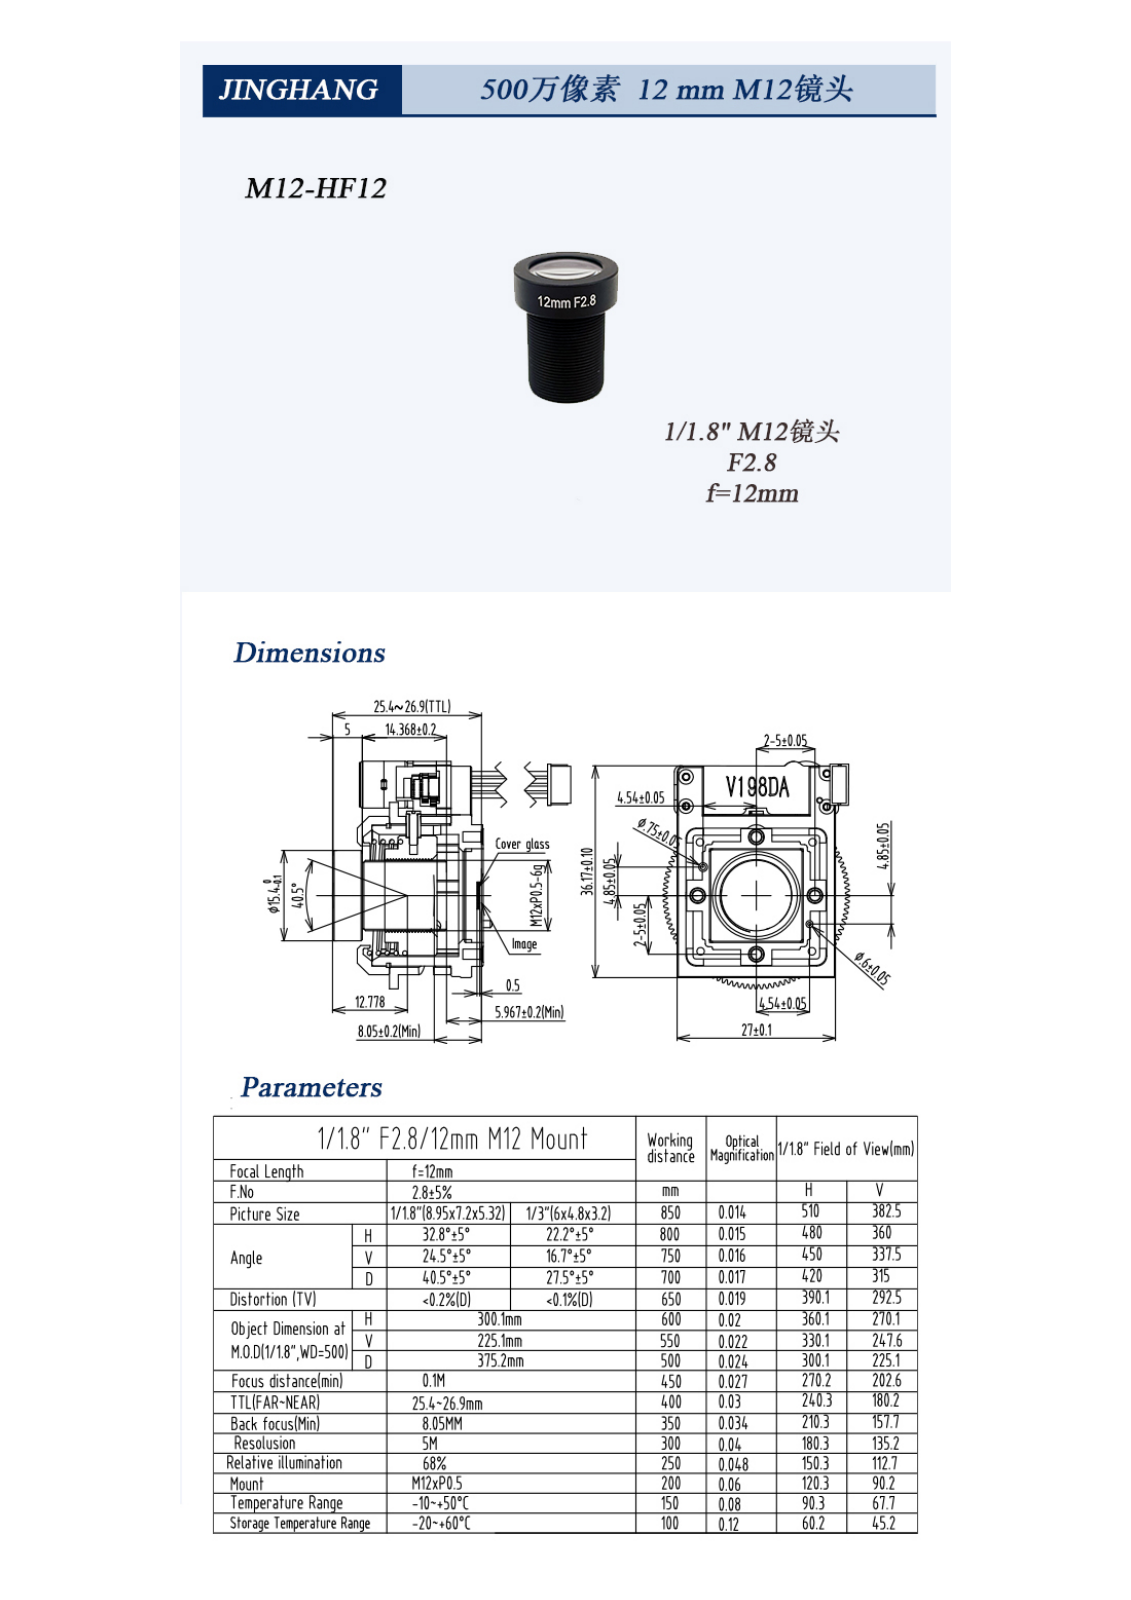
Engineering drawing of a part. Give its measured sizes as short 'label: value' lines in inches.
name: FS1205A-200
written by: PRO/ENGINEER BY PARAMETRIC TECHNOLOGY CORPORATION, 2010370 (CONFIG_CONTROL_DESIGN)
unit: in
bodies: 1 solid, 116 faces (9 planar, 62 cylindrical, 45 other)
size: 0.686 × 0.543 × 0.543
volume: 0.103 in³; area: 1.947 in²
holes: 1× ⌀0.31, 1× ⌀0.348, 1× ⌀0.374, 1× ⌀0.48
bosses: 1× ⌀0.543, 1× ⌀0.472, 1× ⌀0.423, 1× ⌀0.395
face distances: 0.649, 0.492, 0.019, 0.157, 0.176, 0.472, 0.683, 0.526, 0.506, 0.034
